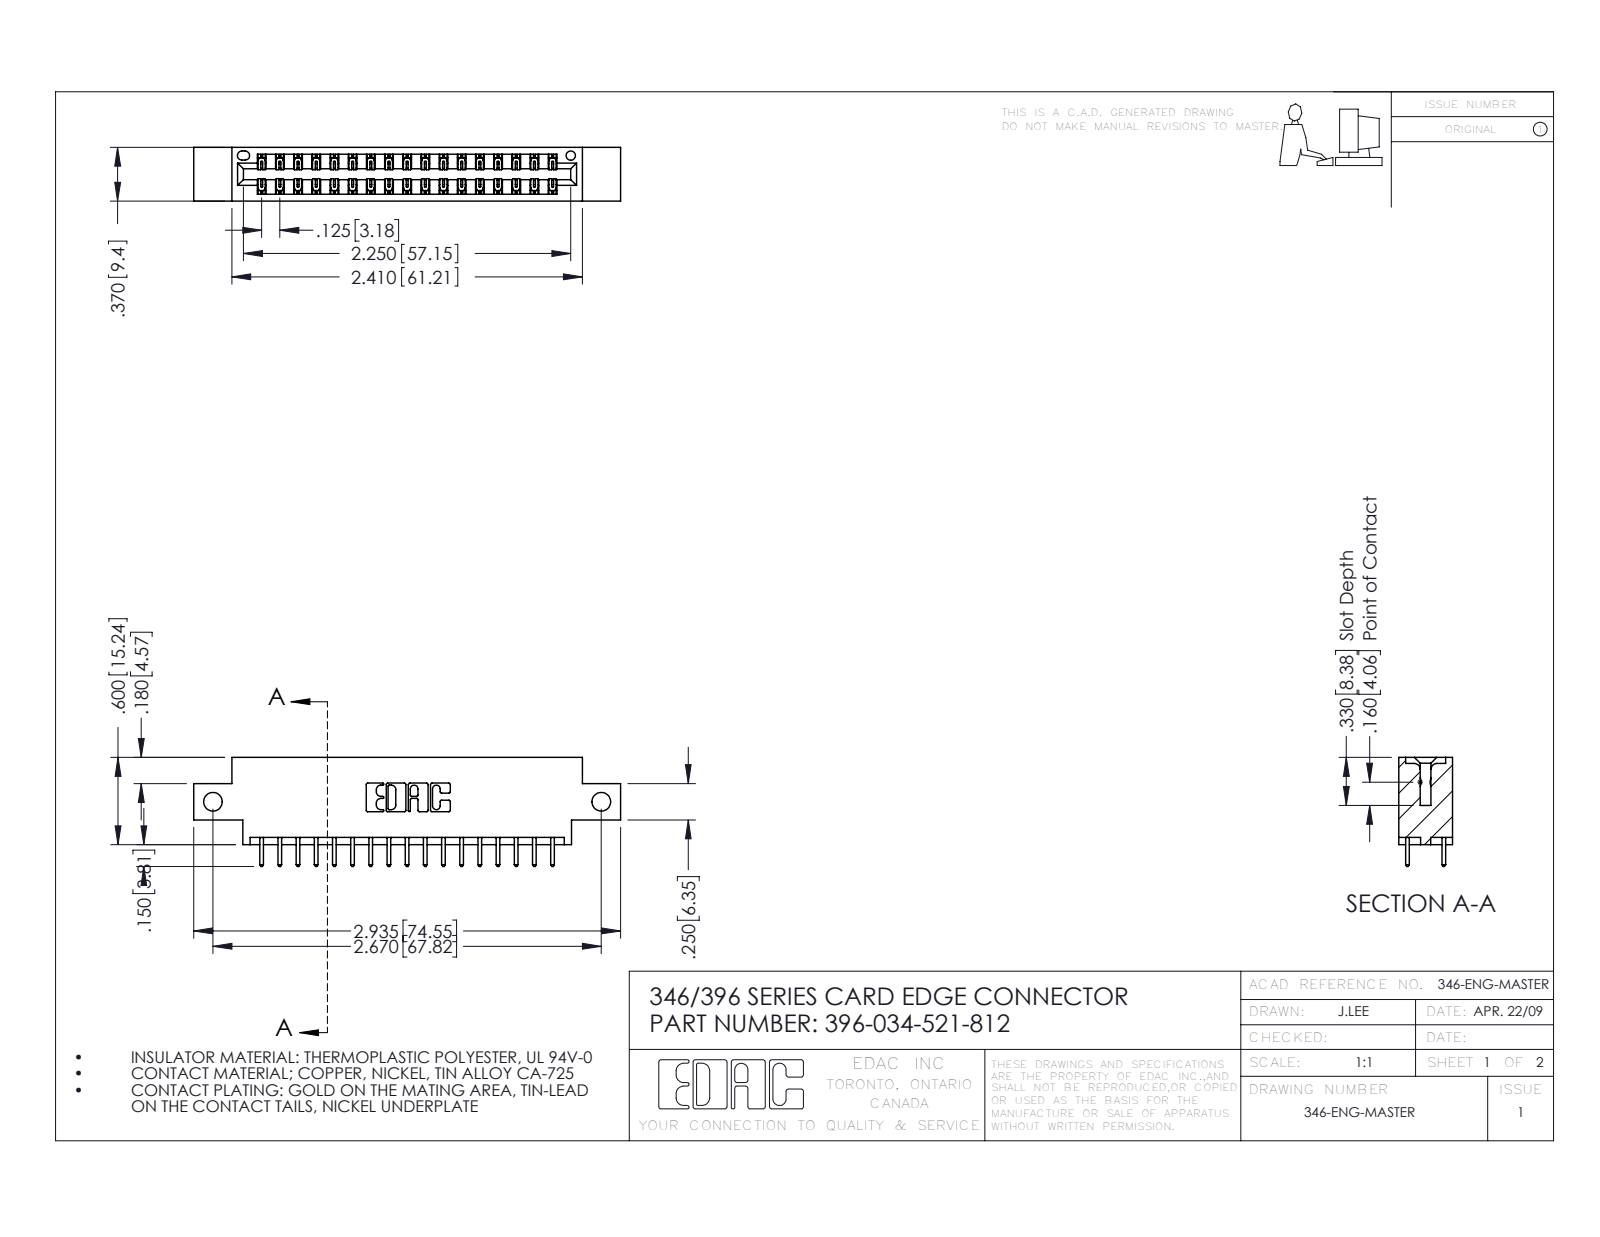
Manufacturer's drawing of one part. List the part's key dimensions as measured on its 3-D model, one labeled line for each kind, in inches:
Part name (STEP PRODUCT): 396-034-521-812; 345-292-001_345-293-121; 346 Part_0.170 Offset - Side Mount
STEP written by: SolidWorks 2016 (CONFIG_CONTROL_DESIGN)
Units: inches
Bodies: 35 solids, 1894 faces (1270 planar, 624 cylindrical, 0 other)
Overall size (bounding box): 2.935 × 0.75 × 0.37
Volume: 0.416 in³ · Surface area: 13.84 in²
Round holes (diameter × count): ⌀0.128 ×2, ⌀0.064 ×1
Partial cylindrical surfaces — rounded edges, fillets, slot ends (radius × count): R0.006 ×51, R0.01 ×34, R0.01 ×22, R0.007 ×6, R0.031 ×6, R0.026 ×3, R0.014 ×2, R0.022 ×2
Main face-to-face distances: 0.048, 0.322, 0.25, 0.37, 0.072, 0.298, 0.025, 0.275, 0.148, 0.222
Hole centre spacings: 2.67
